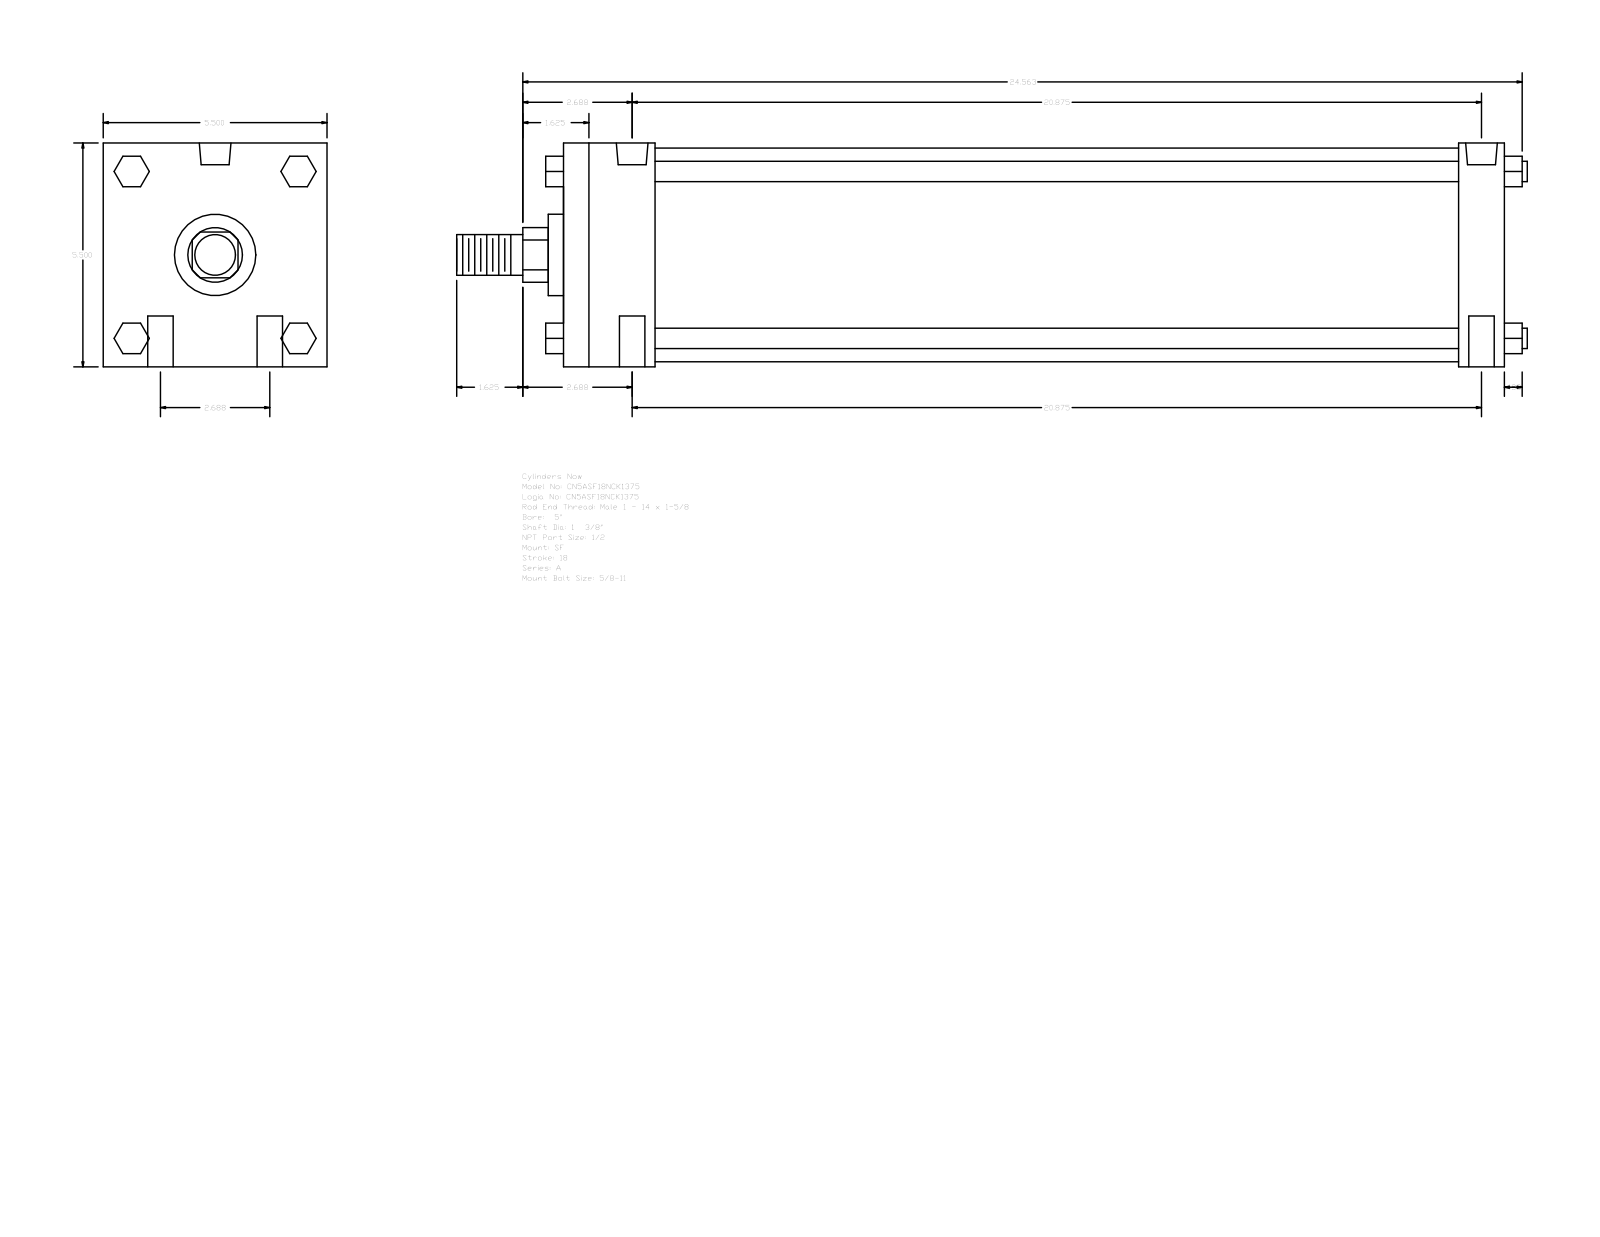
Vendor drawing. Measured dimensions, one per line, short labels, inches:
name: A_SF__0500_1.375
written by: GSSL Pune (CONFIG_CONTROL_DESIGN)
unit: in
bodies: 0 solids, 124 faces (94 planar, 30 cylindrical, 0 other)
size: 26.313 × 5.5 × 5.5
holes: 4× ⌀0.625, 2× ⌀0.344, 2× ⌀0.778
bosses: 4× ⌀0.5, 1× ⌀5.25, 1× ⌀2, 1× ⌀1.375, 1× ⌀1
rounds: 1× R0.672
face distances: 5.5, 23.125, 2.25, 22, 19.75, 20.875, 1.125, 0.75, 2.05, 3.55
hole spacings: 1.344, 20.919, 20.875, 2.687, 21.048, 20.687
